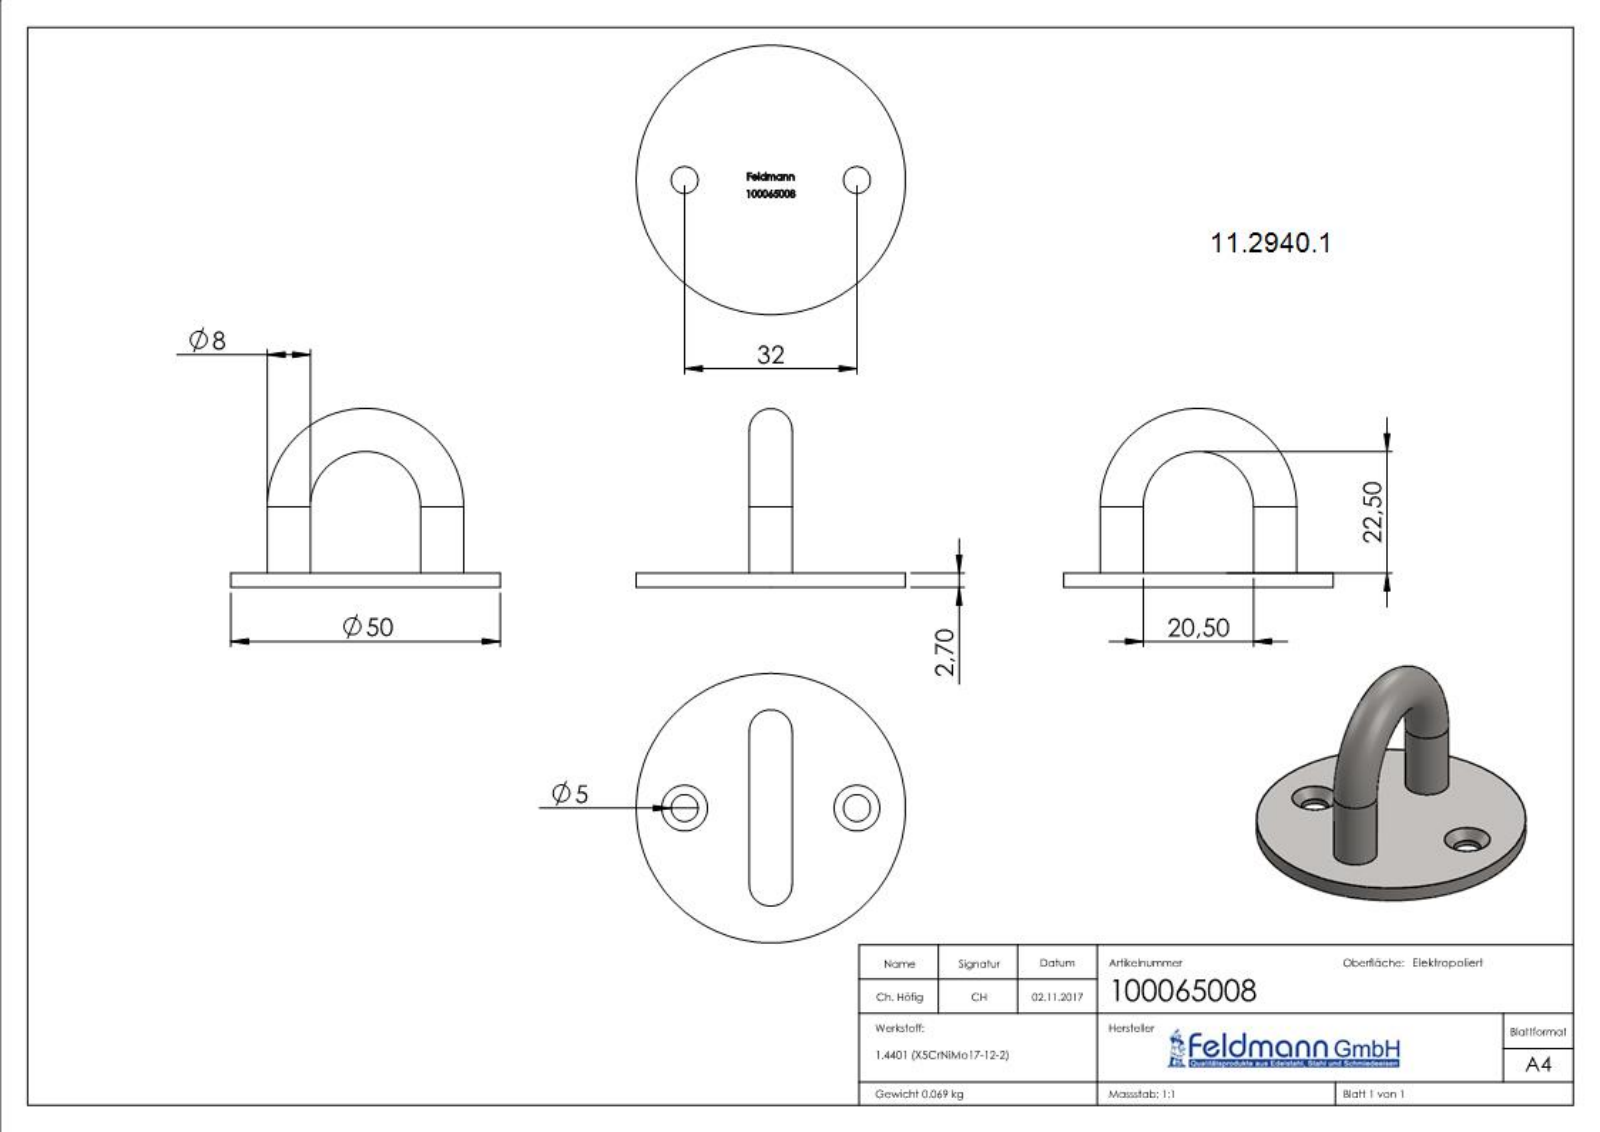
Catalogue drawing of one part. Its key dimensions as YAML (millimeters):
part_name: "100065008"
step_written_by: "SolidWorks 2015 (CONFIG_CONTROL_DESIGN)"
units: millimeters
bodies: {solids: 1, faces: 242, planar: 99, cylindrical: 10, other: 133}
overall_size: [50, 50, 33.2]
volume: 8617
surface_area: 5984
round_holes:
  - {diameter: 5, count: 2}
round_bosses_or_shafts:
  - {diameter: 8, count: 2}
  - {diameter: 50, count: 1}
face_to_face_distances: [2.7, 2.6, 0.39, 2.97, 1.12, 3.11, 3.5, 6.47, 4.09, 2.02]
hole_center_spacings: [32]
